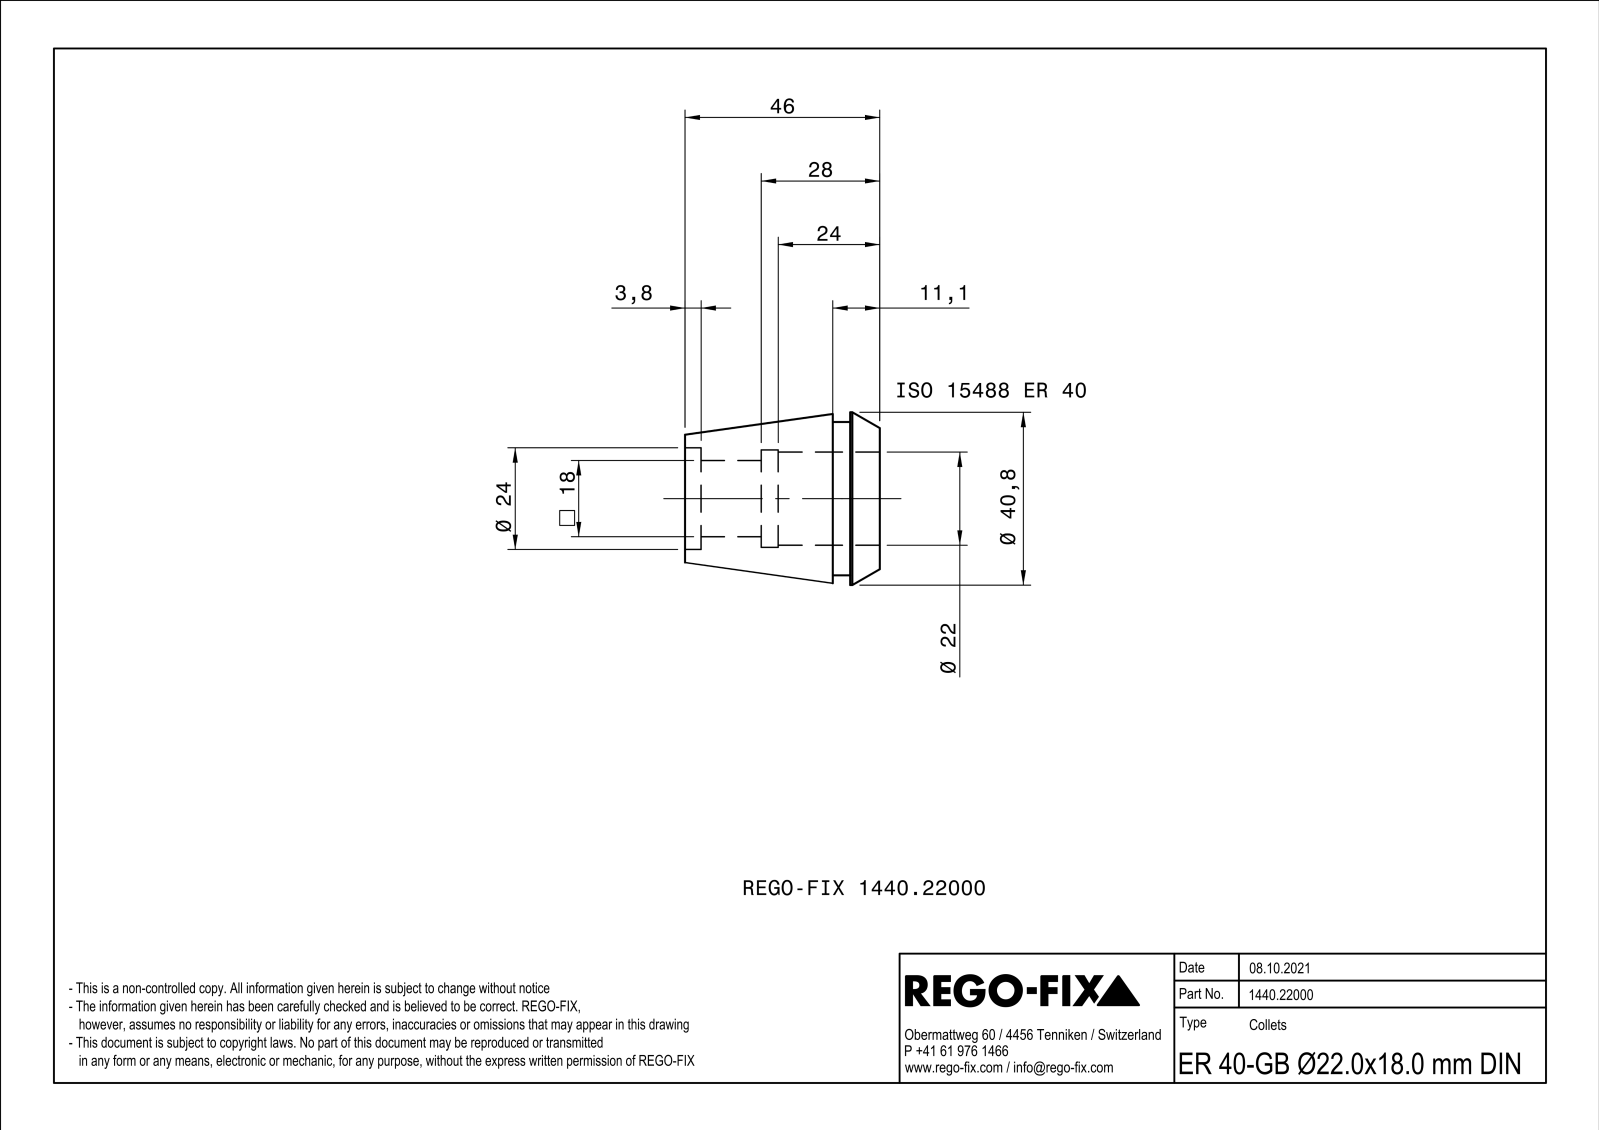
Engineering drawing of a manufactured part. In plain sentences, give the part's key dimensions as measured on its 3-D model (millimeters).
The part is named "NOCUT". Its 3-D file was written by "SIEMENS PLM Software Solid Edge ST10 (AUTOMOTIVE_DESIGN)". It is 1 solid with 168 faces: 60 planar, 48 cylindrical and 60 other. Overall it measures 46 by 40.79 by 40.79 millimeters. Its volume is 26 093 cubic millimeters and its surface area 13 523 square millimeters. Round holes: 1 of diameter 22, 1 of diameter 23, 1 of diameter 23.5, 1 of diameter 24. Round bosses or shafts: 1 of diameter 40.8, 1 of diameter 36.2. Partial cylindrical surfaces (rounded edges, fillets, slot ends): 1 of radius 10.25, 1 of radius 11.4. The main face-to-face distances are 1, 7, 8.8, 9.8, 46, 39, 11.1, 4.1, 34.9, 18.6.
